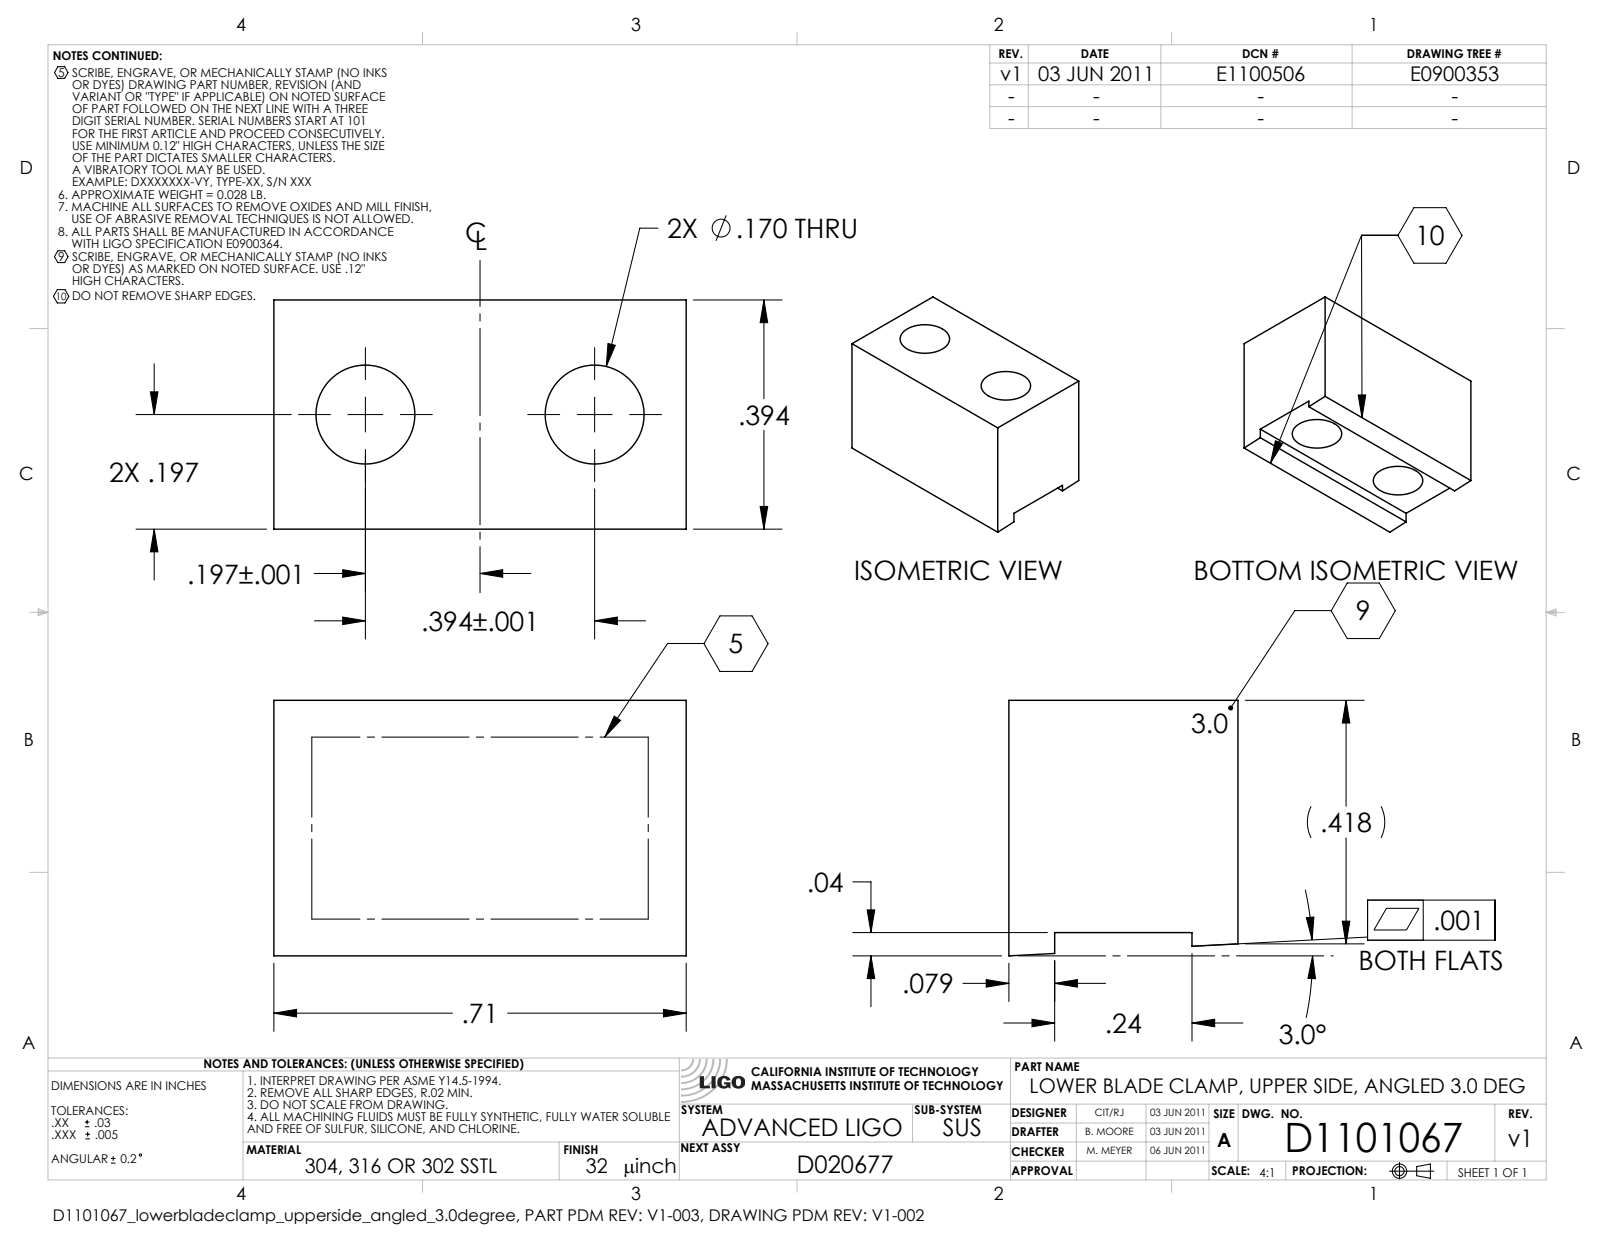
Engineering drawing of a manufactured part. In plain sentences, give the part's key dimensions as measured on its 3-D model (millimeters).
The part is named "D1101067-v1_lowerbladeclamp_upperside_angled_3.0degree". Its 3-D file was written by "SolidWorks 2010 (AUTOMOTIVE_DESIGN)". It is 1 solid with 14 faces: 10 planar, 4 cylindrical and 0 other. Overall it measures 18 by 11.2 by 10 millimeters. Its volume is 1 600 cubic millimeters and its surface area 1 205 square millimeters. Round holes: 2 of diameter 4.3. The main face-to-face distances are 10, 18, 10.1, 2, 8, 8, 6, 2. The hole center spacings are 10.
